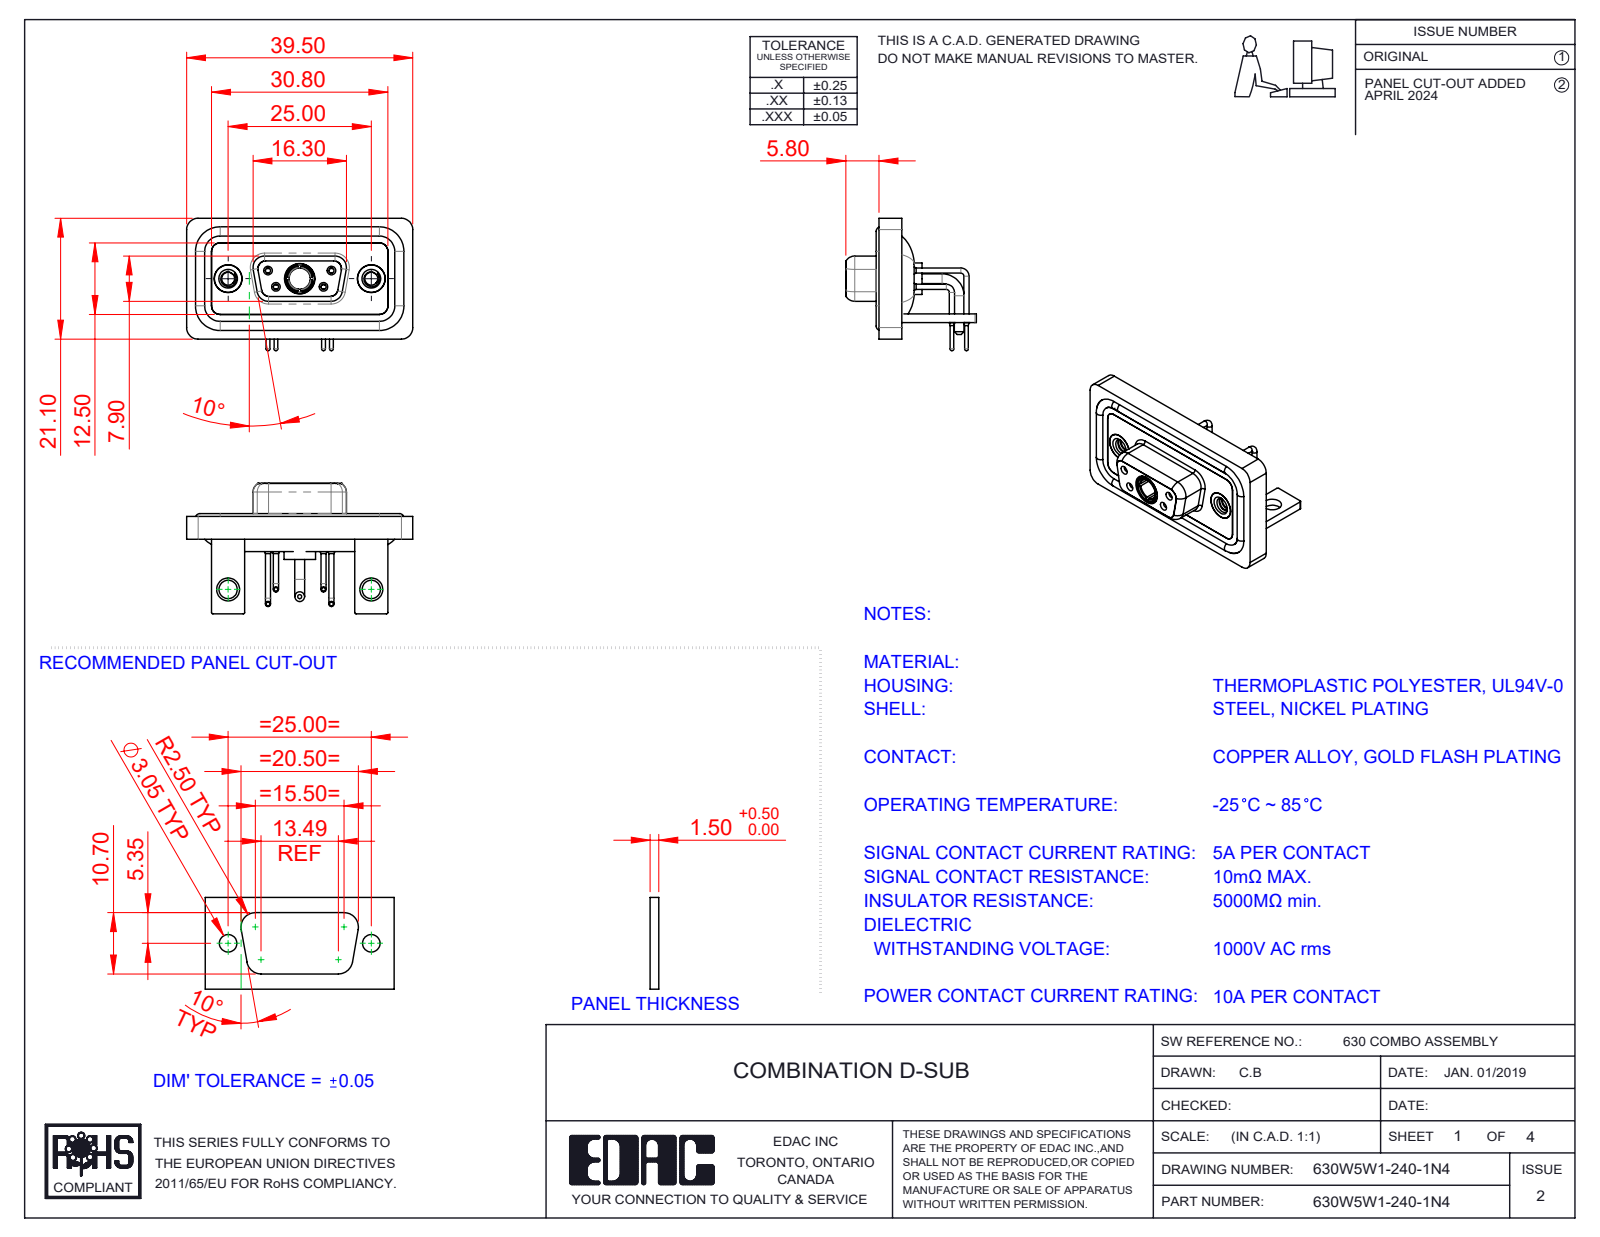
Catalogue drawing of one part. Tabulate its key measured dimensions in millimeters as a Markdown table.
| quantity | value |
| --- | --- |
| part name | 630W5W1-140-1N4; 630Combo Threaded Rivet_2; 630Combo Contact Row 2_50 Contacts; 630Combo Shell Rear_09 Contacts (+6 more) |
| STEP written by | SolidWorks 2023 (CONFIG_CONTROL_DESIGN) |
| units | millimeters |
| bodies | 15 solids, 724 faces (214 planar, 329 cylindrical, 181 other) |
| overall size | 39.5 × 23.12 × 22.8 |
| volume | 5 138 mm³ |
| surface area | 8 528 mm² |
| round holes (diameter × count) | 0.9 × 4, 1.1 × 4, 1.5 × 4, 2 × 4, 4.85 × 3, 1.6 × 2, 1.7 × 2, 2.26 × 2, 3.2 × 2, 4 × 2, 4.05 × 2, 5 × 2 |
| round bosses / shafts (diameter × count) | 1.6 × 6, 0.9 × 4, 0.65 × 4, 4.95 × 2, 4.8 × 2, 1.7 × 2, 5.5 × 1, 5.2 × 1 |
| partial cylindrical surfaces (radius × count) | 2 × 19, 1.5 × 18, 0.25 × 16, 1.35 × 8, 1.6 × 8, 0.5 × 5, 0.6 × 4, 0.65 × 4 |
| main face-to-face distances | 0.4, 2.9, 1.5, 1.8, 1.1, 3.7, 1.6, 0.8, 2.5, 3.1 |
| hole center spacings | 3.16, 5.72, 7.1, 12.5, 18.1, 25, 4.39, 4.4 |
